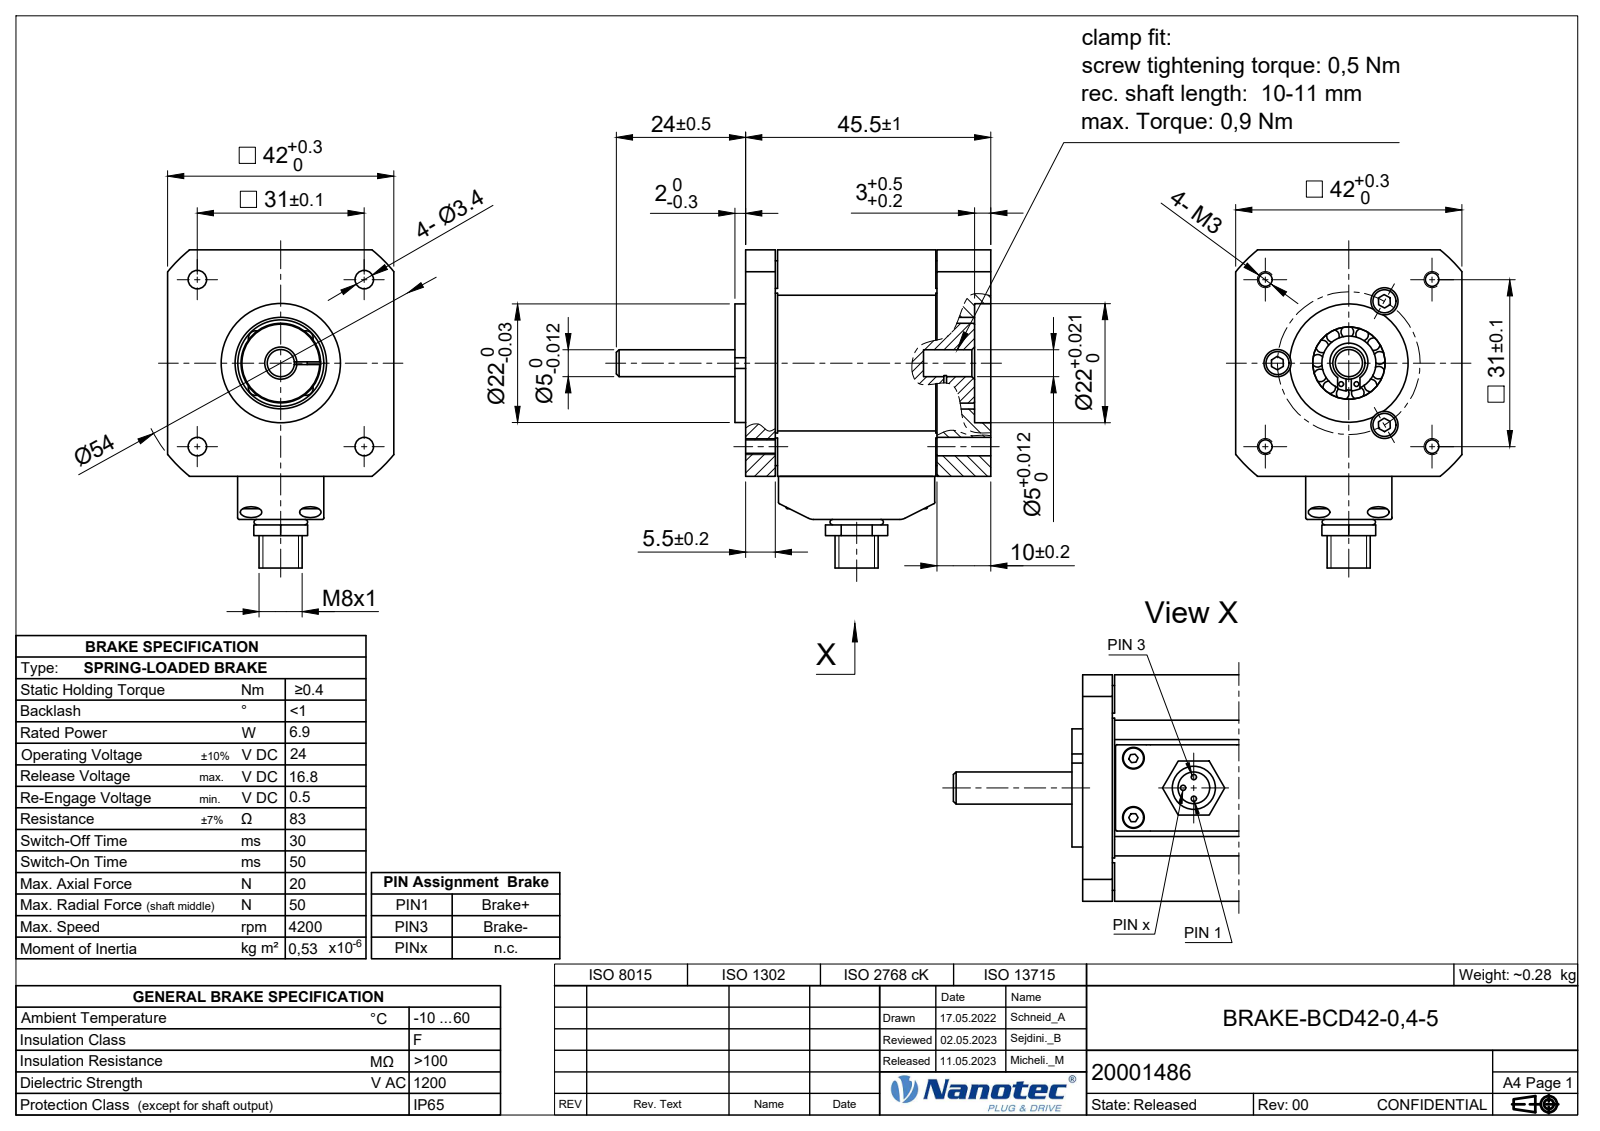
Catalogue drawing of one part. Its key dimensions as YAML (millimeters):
part_name: "BRAKE-BCD42-0,4-5"
step_written_by: "Autodesk Inventor 2021 (AUTOMOTIVE_DESIGN)"
units: millimeters
bodies: {solids: 1, faces: 239, planar: 125, cylindrical: 92, other: 22}
overall_size: [69.5, 58.66, 42]
volume: 70612
surface_area: 14255
round_holes:
  - {diameter: 2.46, count: 4}
  - {diameter: 3.4, count: 4}
  - {diameter: 4, count: 4}
  - {diameter: 2.5, count: 3}
  - {diameter: 5, count: 3}
  - {diameter: 0.9, count: 2}
  - {diameter: 3, count: 1}
  - {diameter: 5.88, count: 1}
  - {diameter: 13.45, count: 1}
  - {diameter: 22.1, count: 1}
round_bosses_or_shafts:
  - {diameter: 3.8, count: 4}
  - {diameter: 4.3, count: 3}
  - {diameter: 1, count: 3}
  - {diameter: 38, count: 1}
  - {diameter: 22, count: 1}
  - {diameter: 8, count: 1}
  - {diameter: 7.04, count: 1}
  - {diameter: 6, count: 1}
partial_cylinders:
  - {radius: 0.3, count: 12}
  - {radius: 1, count: 12}
  - {radius: 3, count: 4}
  - {radius: 2, count: 2}
  - {radius: 5.2, count: 1}
  - {radius: 21, count: 1}
  - {radius: 27, count: 1}
face_to_face_distances: [45.5, 42, 5.5, 40, 29, 13, 3, 37, 42.5, 30]
hole_center_spacings: [30.99, 12.48, 21.91, 21.92, 22.94, 30.98, 31, 43.83]
